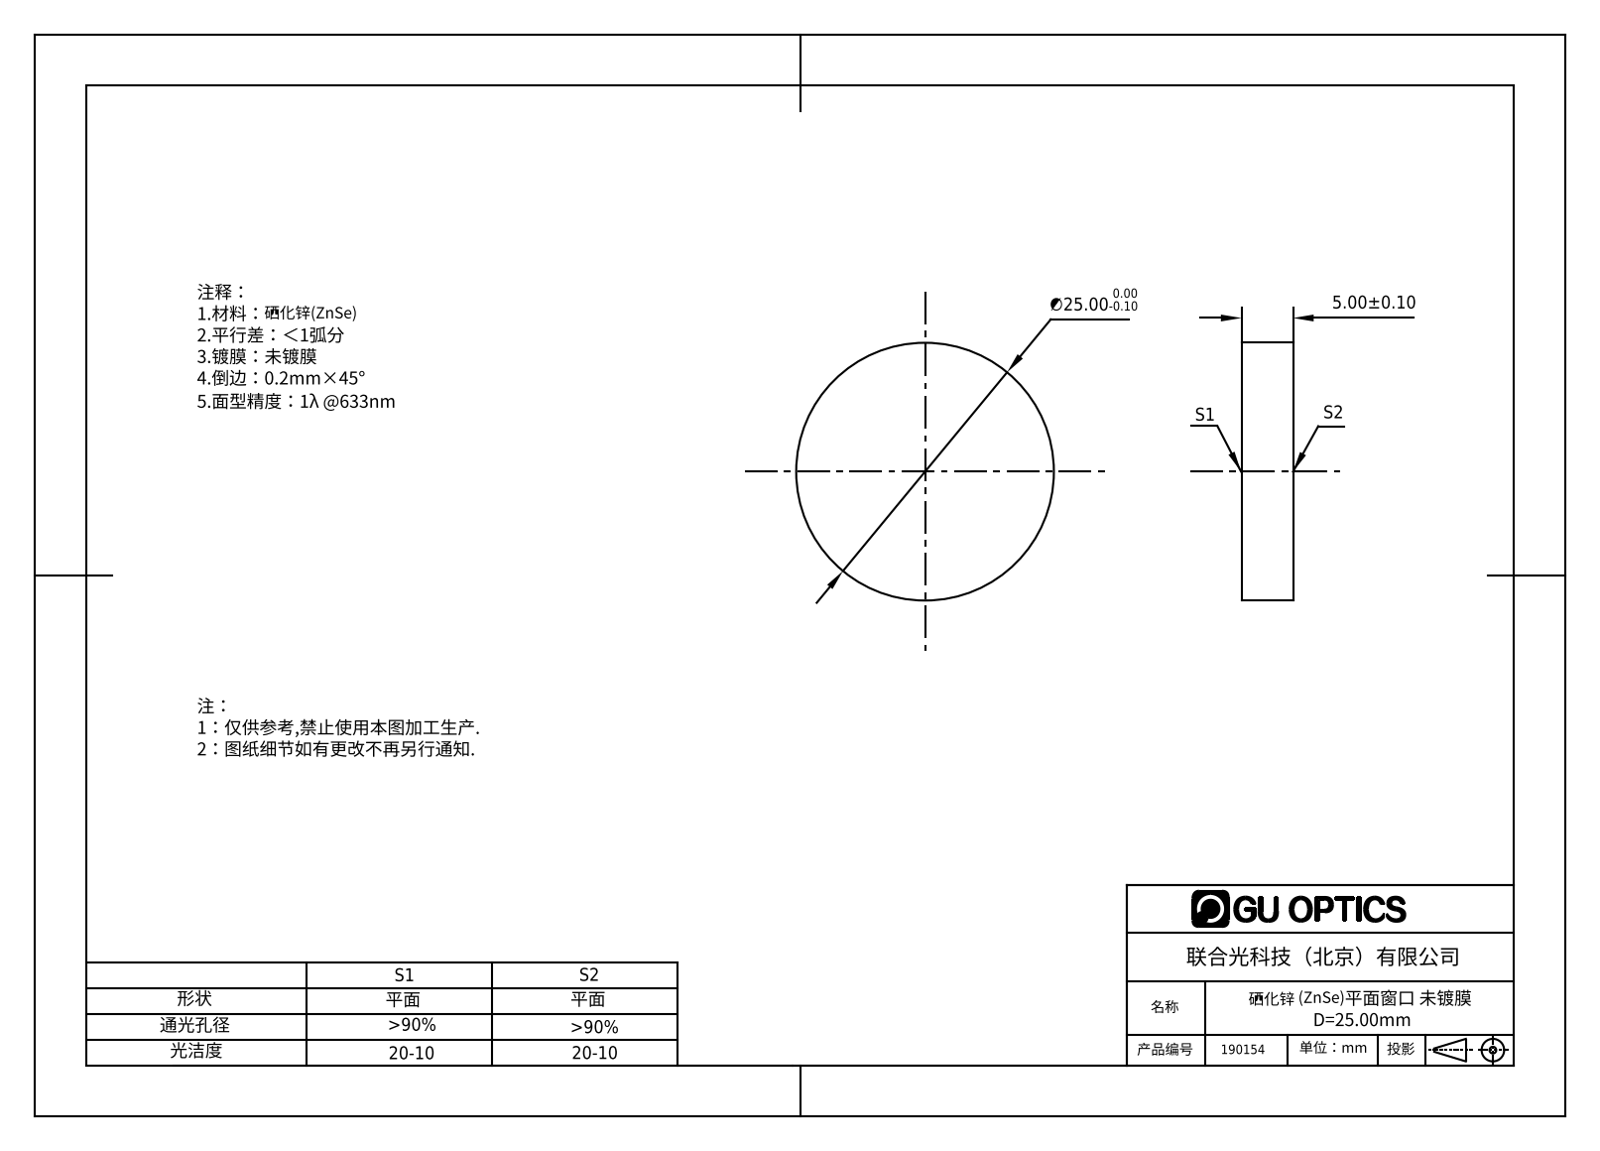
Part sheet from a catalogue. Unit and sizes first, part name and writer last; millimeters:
Units: millimetres
Overall size (bounding box): 25 × 25 × 5
Round bosses / shafts (diameter × count): ⌀25 ×1
Main face-to-face distances: 5
Volume: 2 454 mm³ · Surface area: 1 374 mm²
Bodies: 1 solid, 4 faces (2 planar, 2 cylindrical, 0 other)
Part name (STEP PRODUCT): 190154
STEP written by: SolidWorks 2016 (AUTOMOTIVE_DESIGN)
